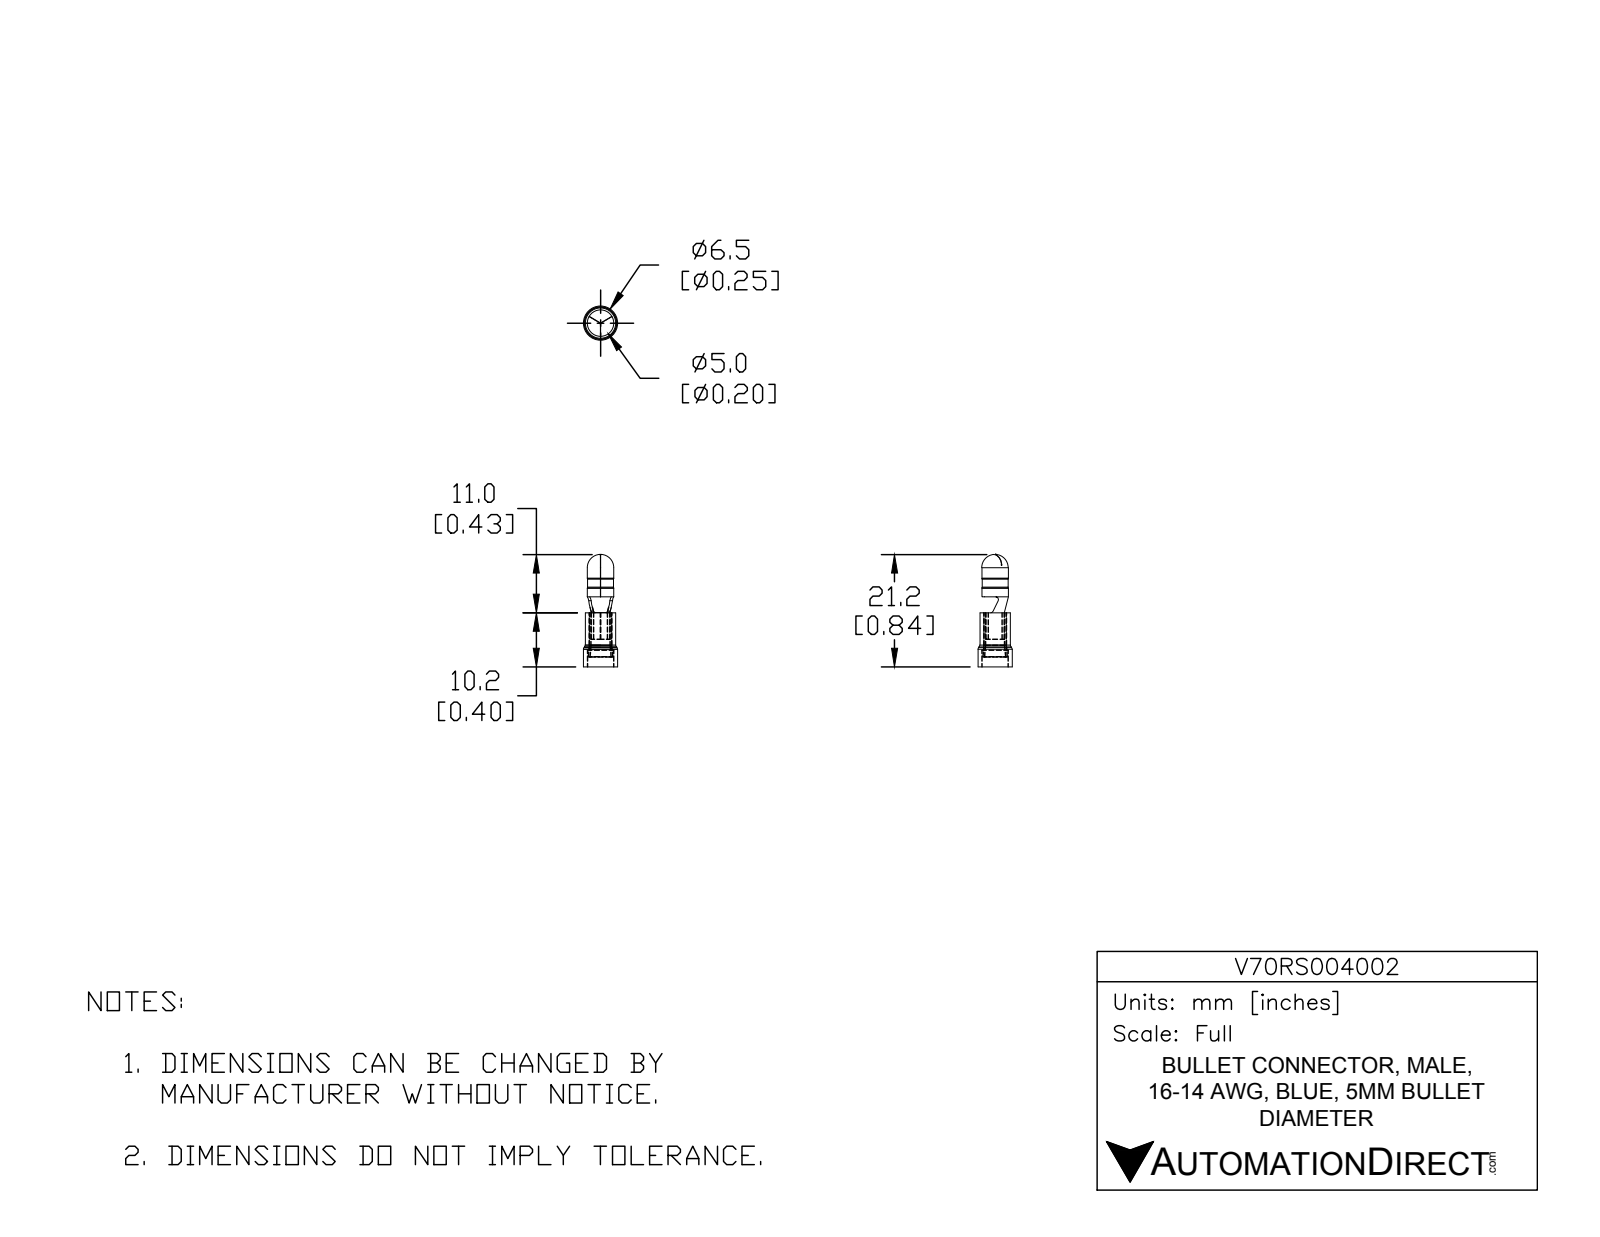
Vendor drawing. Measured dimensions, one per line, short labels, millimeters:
name: V70RS004002
written by: SolidWorks 2017 (AUTOMOTIVE_DESIGN)
unit: mm
bodies: 3 solids, 92 faces (24 planar, 33 cylindrical, 35 other)
size: 21.23 × 6.45 × 6.45
volume: 238 mm³; area: 966 mm²
holes: 1× ⌀2.6, 1× ⌀3.6, 1× ⌀4.1, 1× ⌀4.25, 1× ⌀4.95
bosses: 1× ⌀6.45, 1× ⌀5.75, 1× ⌀5, 1× ⌀4.9, 1× ⌀4.2, 1× ⌀3.5
rounds: 2× R0.5
face distances: 10.23, 3.15, 7.08, 5.23, 2.08, 5, 13.23, 10.08, 8, 3
